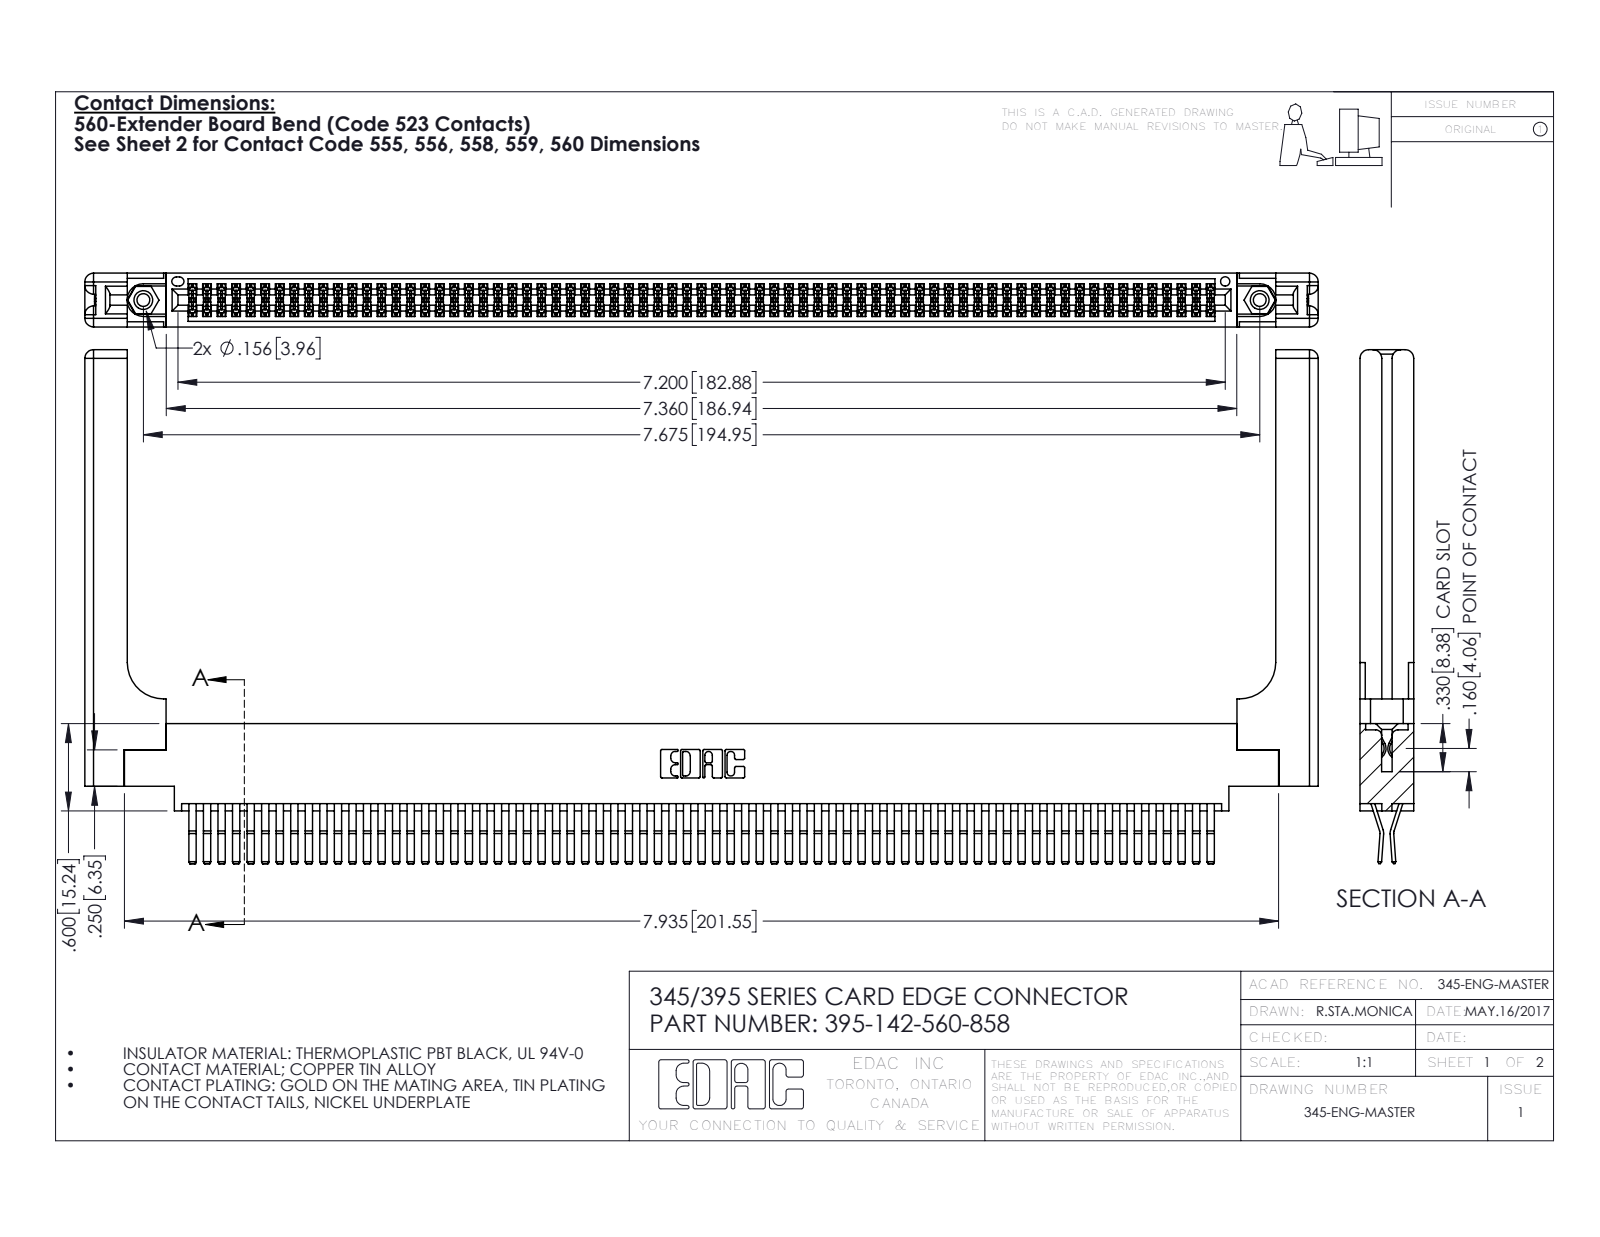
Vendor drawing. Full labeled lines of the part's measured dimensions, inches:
Part name (STEP PRODUCT): 345-292-001_560 Tail; 345-220-058_345-220-058; 345 Part_0.170 Offset - 0.156 Dia-TH; 395-142-560-858 (+1 more)
STEP written by: SolidWorks 2016 (CONFIG_CONTROL_DESIGN)
Units: inches
Bodies: 147 solids, 7770 faces (4918 planar, 2792 cylindrical, 60 other)
Overall size (bounding box): 8.479 × 3.532 × 0.37
Volume: 1.86 in³ · Surface area: 63.07 in²
Round holes (diameter × count): ⌀0.089 ×2, ⌀0.125 ×2, ⌀0.156 ×2, ⌀0.064 ×1
Round bosses / shafts (diameter × count): ⌀0.155 ×2
Partial cylindrical surfaces — rounded edges, fillets, slot ends (radius × count): R0.006 ×214, R0.01 ×22, R0.06 ×16, R0.007 ×6, R0.031 ×6, R0.026 ×3, R0.01 ×2, R0.014 ×2
Main face-to-face distances: 0.072, 0.298, 0.025, 0.37, 0.098, 0.272, 0.2, 0.225, 0.175, 0.148
Hole centre spacings: 0.27, 7.439, 7.675
